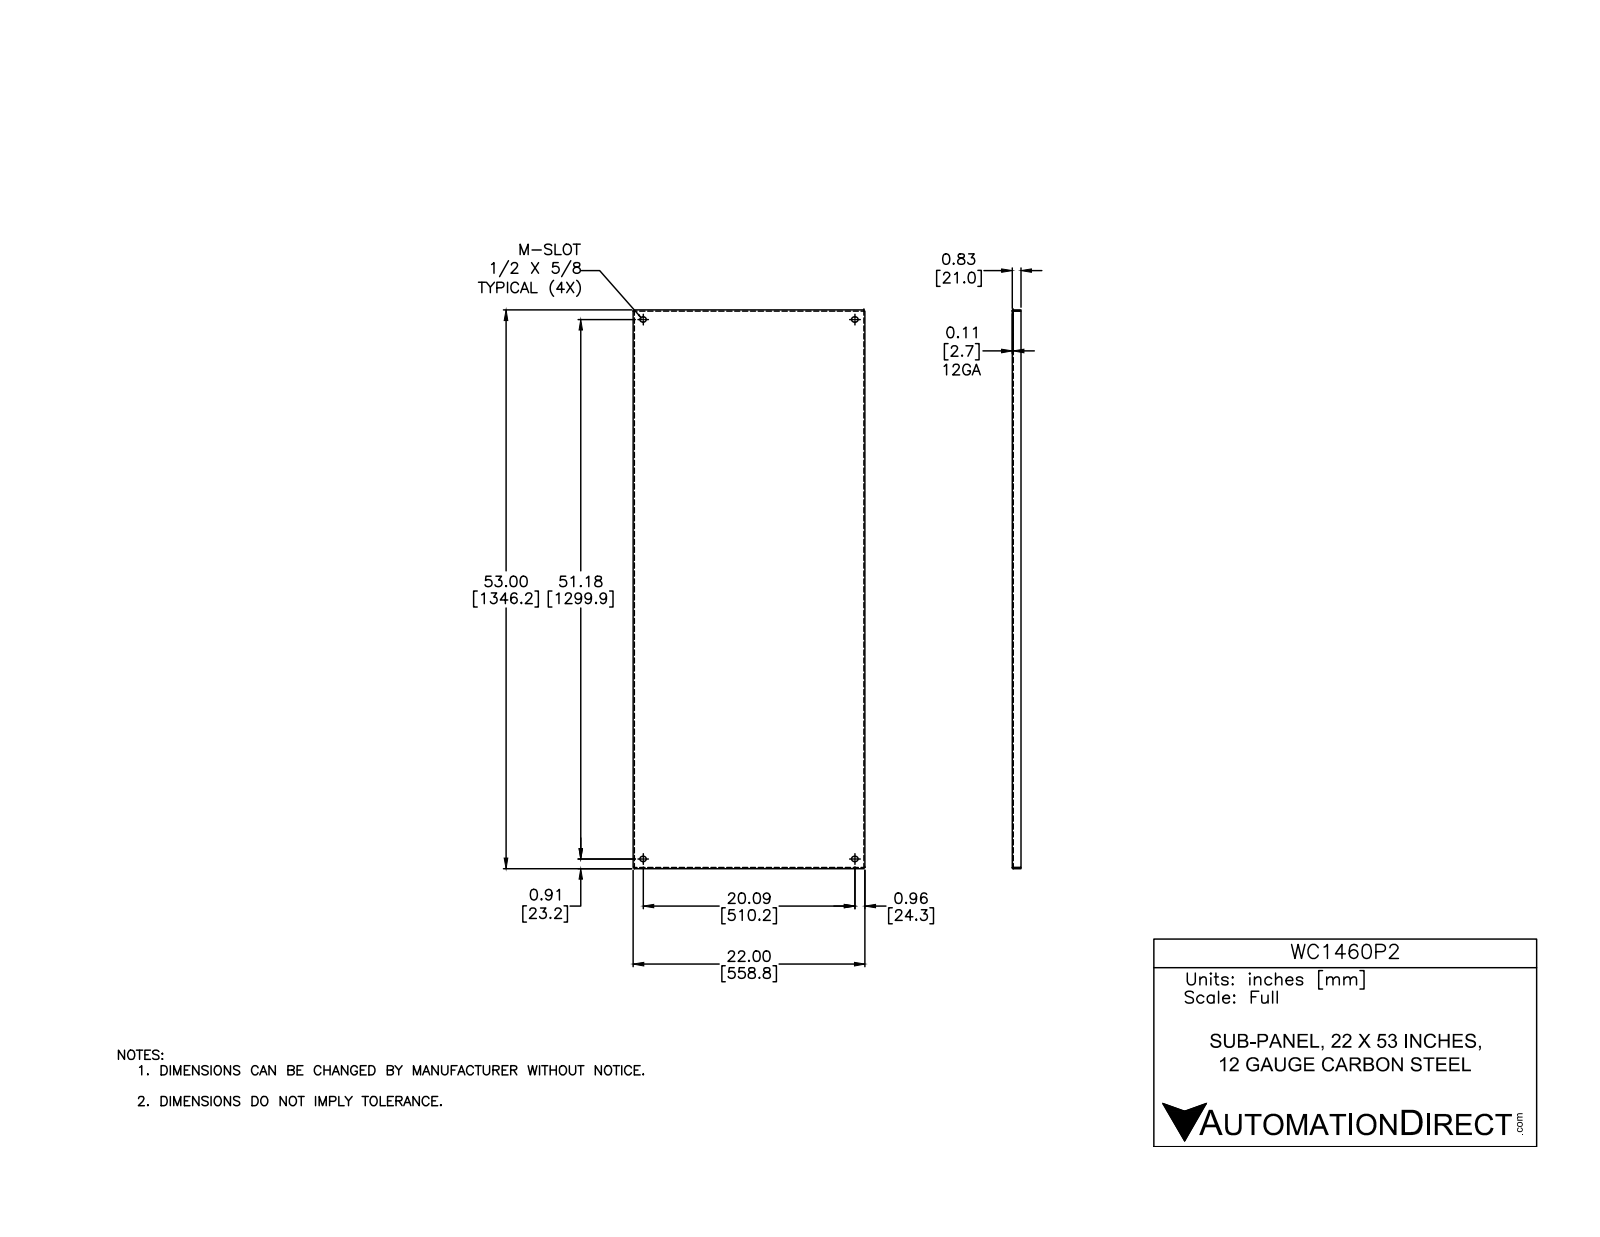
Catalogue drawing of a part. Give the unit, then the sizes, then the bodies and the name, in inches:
Units: inches
Overall size (bounding box): 53 × 22.063 × 0.828
Partial cylindrical surfaces — rounded edges, fillets, slot ends (radius × count): R0.25 ×8, R0.107 ×3, R0.108 ×1
Main face-to-face distances: 0.105, 21.958, 22.063, 21.853, 52.895, 53, 52.791, 0.828, 0.723, 0.112
Volume: 133.1 in³ · Surface area: 2 562 in²
Bodies: 1 solid, 58 faces (30 planar, 20 cylindrical, 8 other)
Part name (STEP PRODUCT): WC1460P2
STEP written by: SolidWorks 2014 (AUTOMOTIVE_DESIGN)
